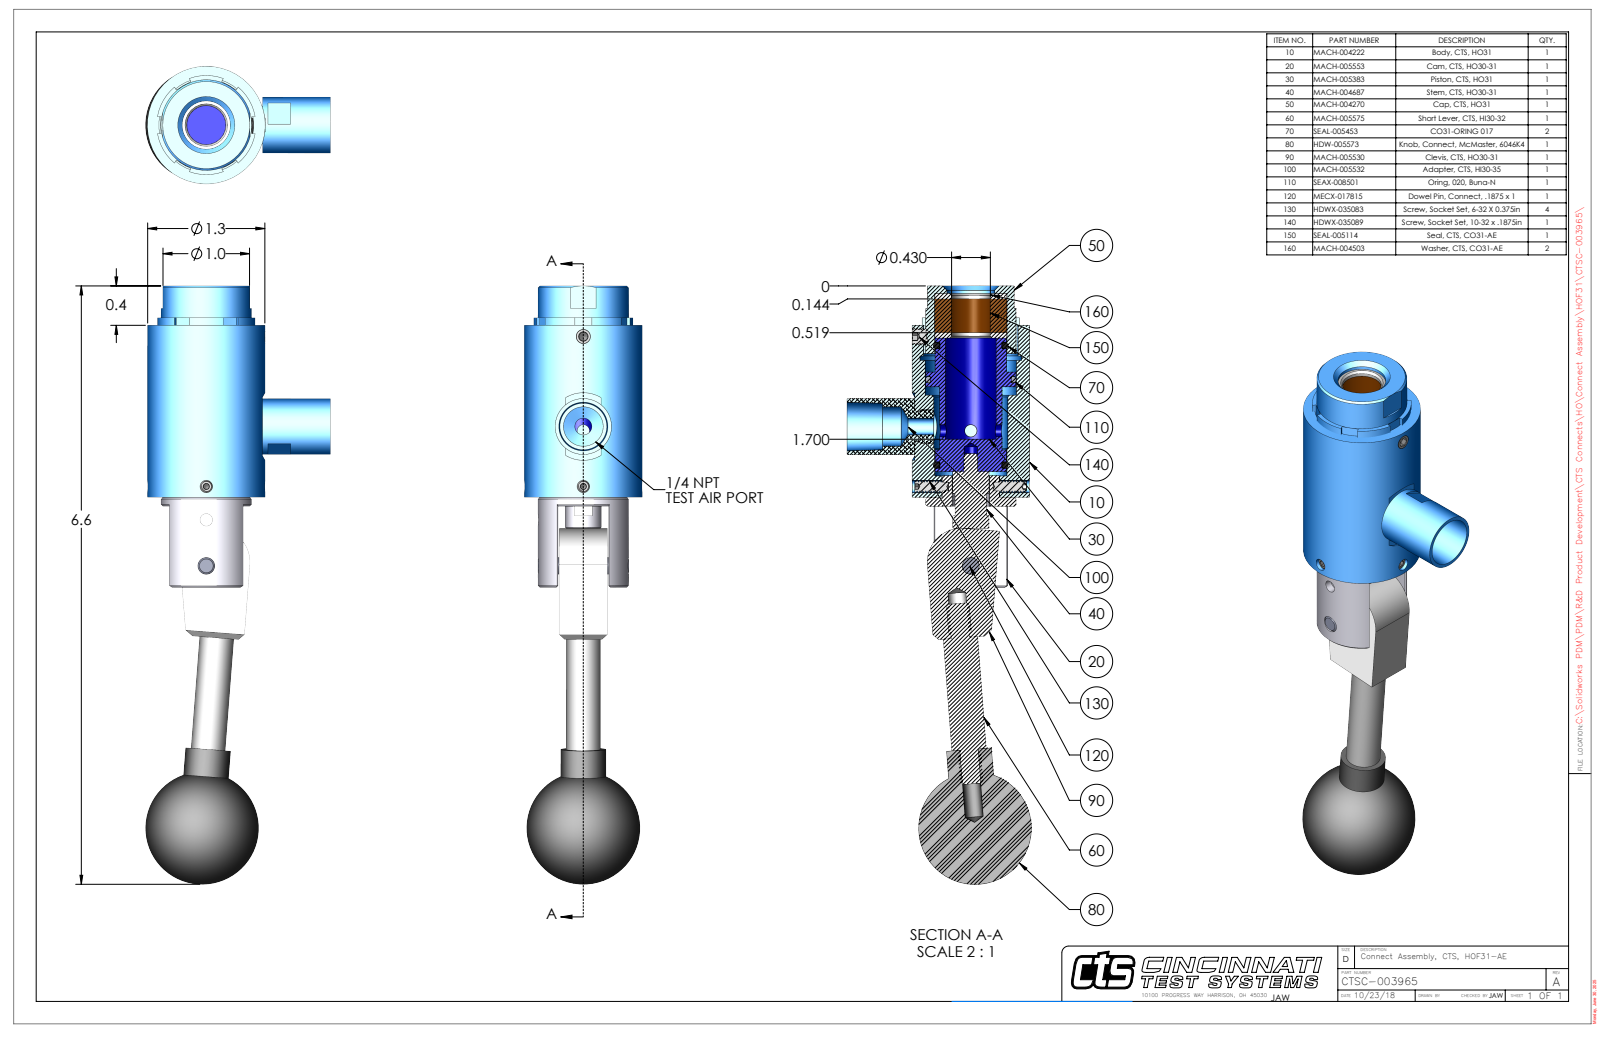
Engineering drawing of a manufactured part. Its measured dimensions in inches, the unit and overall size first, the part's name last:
Units: inches
Overall size (bounding box): 6.636 × 2.042 × 1.3
Round holes (diameter × count): ⌀0.136 ×2, ⌀0.201 ×2, ⌀0.138 ×1, ⌀0.15 ×1, ⌀0.159 ×1, ⌀0.187 ×1, ⌀0.189 ×1, ⌀0.19 ×1, ⌀0.332 ×1, ⌀0.418 ×1, ⌀0.43 ×1, ⌀0.432 ×1
Round bosses / shafts (diameter × count): ⌀0.138 ×2, ⌀1.3 ×1, ⌀1 ×1, ⌀0.792 ×1, ⌀0.79 ×1, ⌀0.69 ×1, ⌀0.63 ×1, ⌀0.62 ×1
Partial cylindrical surfaces — rounded edges, fillets, slot ends (radius × count): R0.374 ×1, R0.375 ×1, R0.524 ×1, R0.547 ×1
Main face-to-face distances: 0.012, 0.542, 0.059, 0.434, 0.53, 0.375, 0.554, 1.825, 2.2, 2.259
Hole centre spacings: 0.047, 0.51, 0.987, 0.997, 1.044, 1.497
Volume: 4.512 in³ · Surface area: 46.27 in²
Bodies: 14 solids, 532 faces (173 planar, 217 cylindrical, 142 other)
Part name (STEP PRODUCT): CTSC-003965
STEP written by: SolidWorks 2023 (AUTOMOTIVE_DESIGN)
